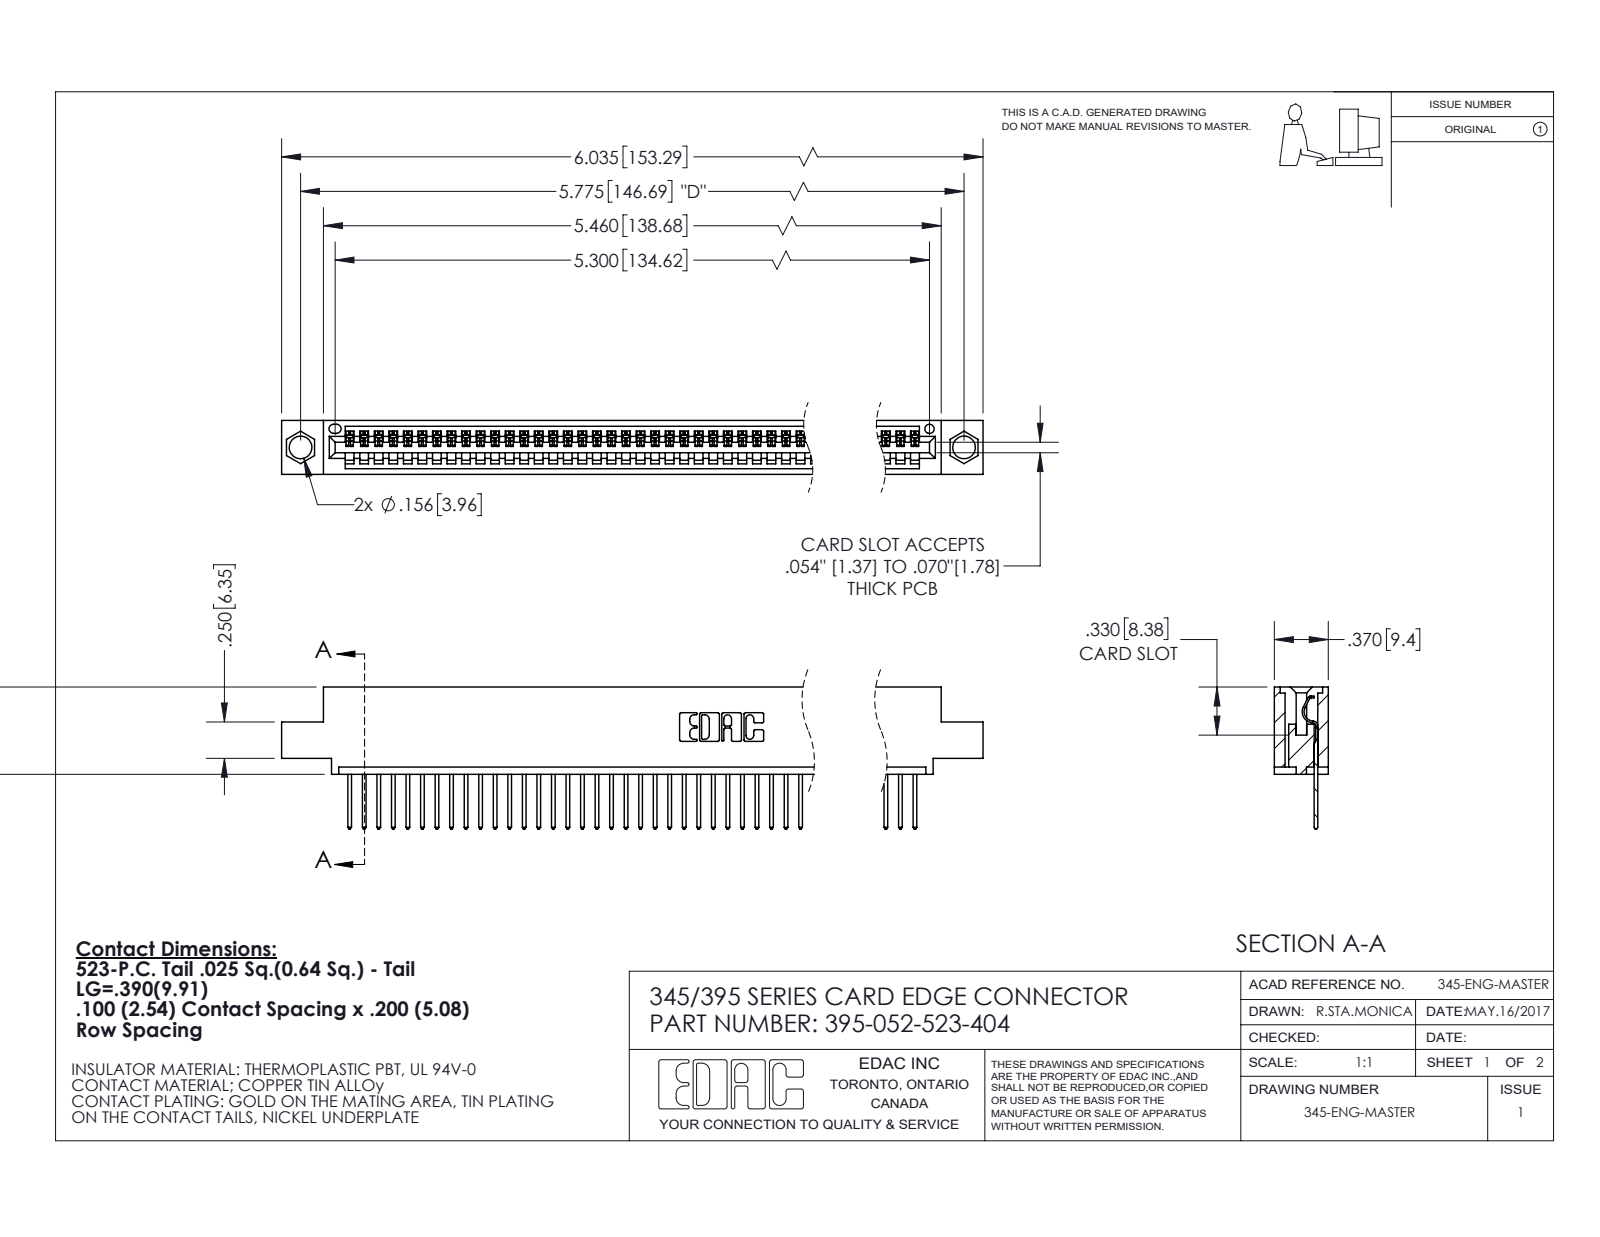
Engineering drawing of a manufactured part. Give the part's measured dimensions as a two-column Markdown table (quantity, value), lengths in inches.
| quantity | value |
| --- | --- |
| part name | 395-052-523-404; 345 Part_0.110 Offset - 0.156 Dia-TI; 345-292-001_345-293-123 |
| STEP written by | SolidWorks 2020 (CONFIG_CONTROL_DESIGN) |
| units | inches |
| bodies | 53 solids, 3160 faces (2178 planar, 982 cylindrical, 0 other) |
| overall size | 6.035 × 0.977 × 0.37 |
| volume | 0.881 in³ |
| surface area | 29.93 in² |
| round holes (diameter × count) | 0.156 × 2, 0.064 × 1 |
| partial cylindrical surfaces (radius × count) | 0.006 × 104, 0.01 × 104, 0.01 × 22, 0.007 × 6, 0.031 × 6, 0.026 × 3, 0.031 × 2, 0.04 × 2 |
| main face-to-face distances | 0.298, 0.072, 0.37, 0.098, 0.272, 0.025, 0.2, 0.225, 0.149, 0.072 |
| hole center spacings | 0.27, 5.539, 5.775 |
